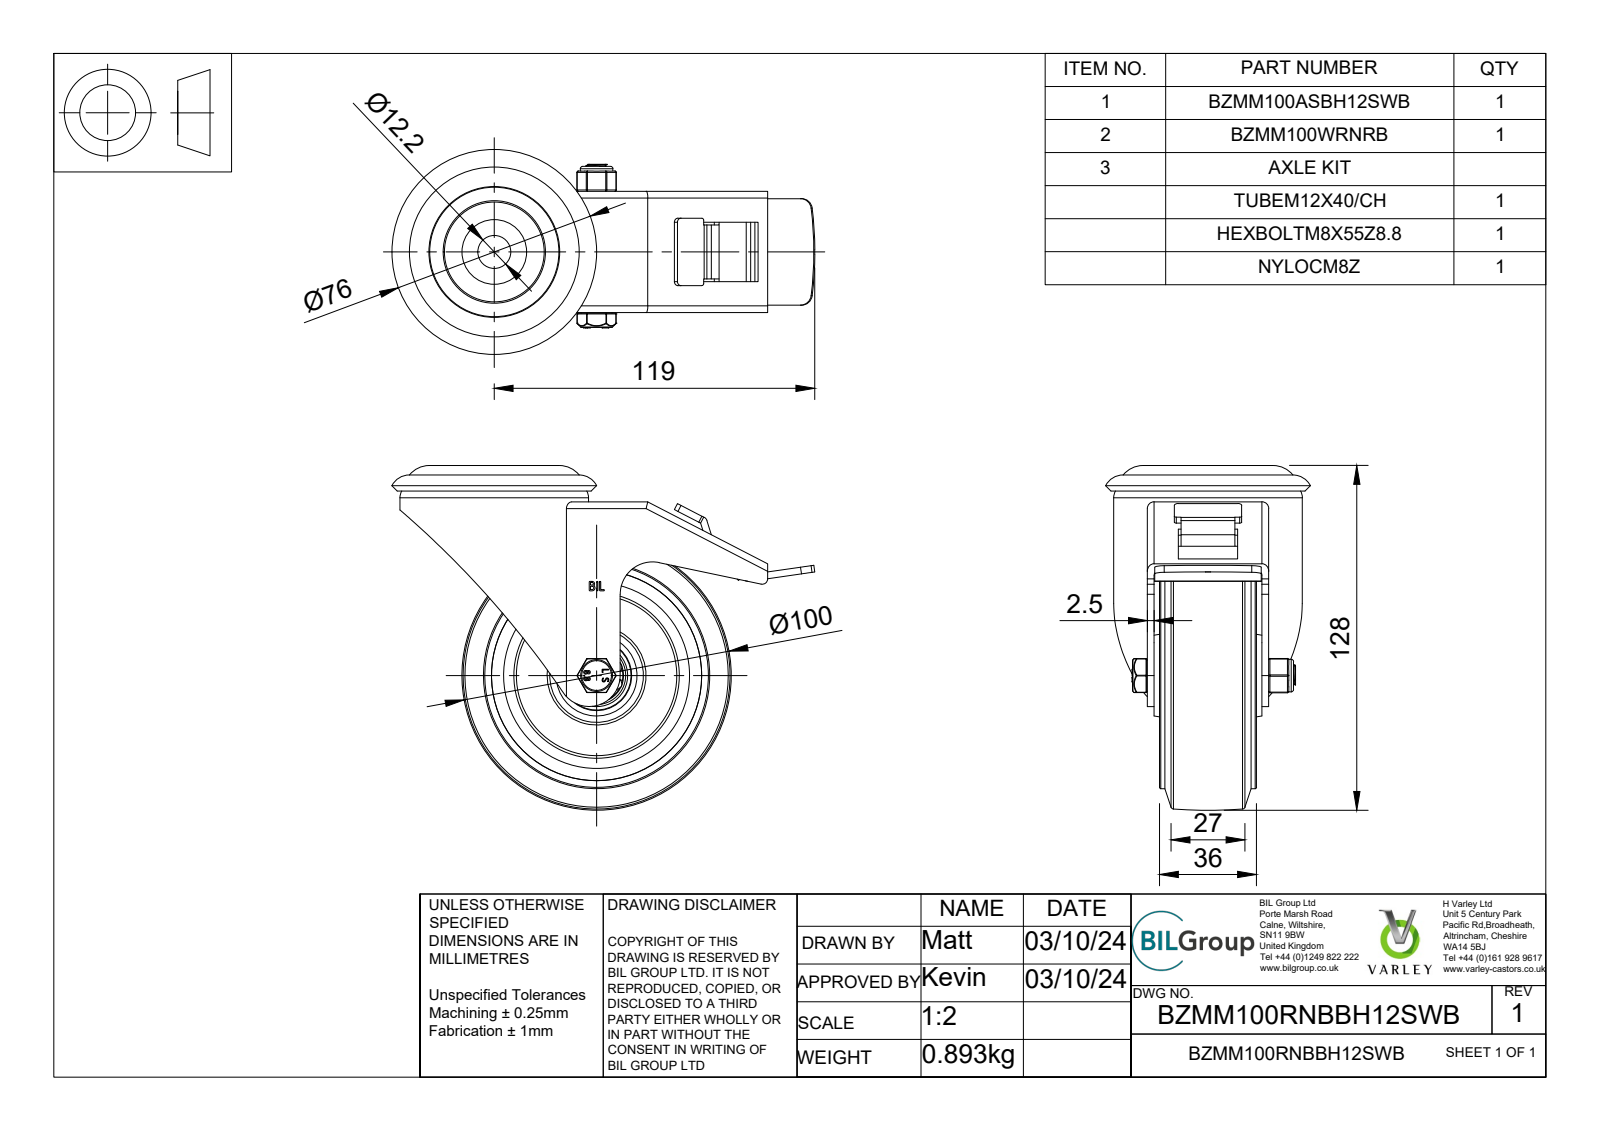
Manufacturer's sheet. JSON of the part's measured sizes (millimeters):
{"part_name": "BZMM100RNBBH12SWB v3; BZMM100ASBH12SWB v1; PRESSED STEEL, ZINC PLATED HEAD; PRESSED STEEL, ZINC PLATED FORKS (+8 more)", "step_written_by": "Autodesk Translation Framework v13.20.0.188 (AUTOMOTIVE_DESIGN)", "units": "millimeters", "bodies": {"solids": 19, "faces": 674, "planar": 340, "cylindrical": 225, "other": 109}, "overall_size": [157, 128, 76], "volume_mm3": 275727, "surface_area_mm2": 126905, "round_holes": [[0.66, 2], [8, 1], [8.2, 1], [8.4, 1], [8.6, 1], [12.2, 1], [12.5, 1], [20, 1], [26, 1], [65, 1], [72, 1], [78, 1]], "round_bosses_or_shafts": [[3.75, 8], [84, 1], [70, 1], [49.5, 1], [38, 1], [24, 1], [21.31, 1], [19.5, 1]], "partial_cylinders_radius": [[0.75, 50], [0.5, 18], [0.25, 12], [1.25, 10], [0.33, 4], [0.64, 4], [2.5, 4], [2, 3]], "face_to_face_distances": [2.5, 4.5, 2, 42.5, 23, 15, 27.5, 13, 40.5, 17.5], "hole_center_spacings": [3.22, 2.49]}
